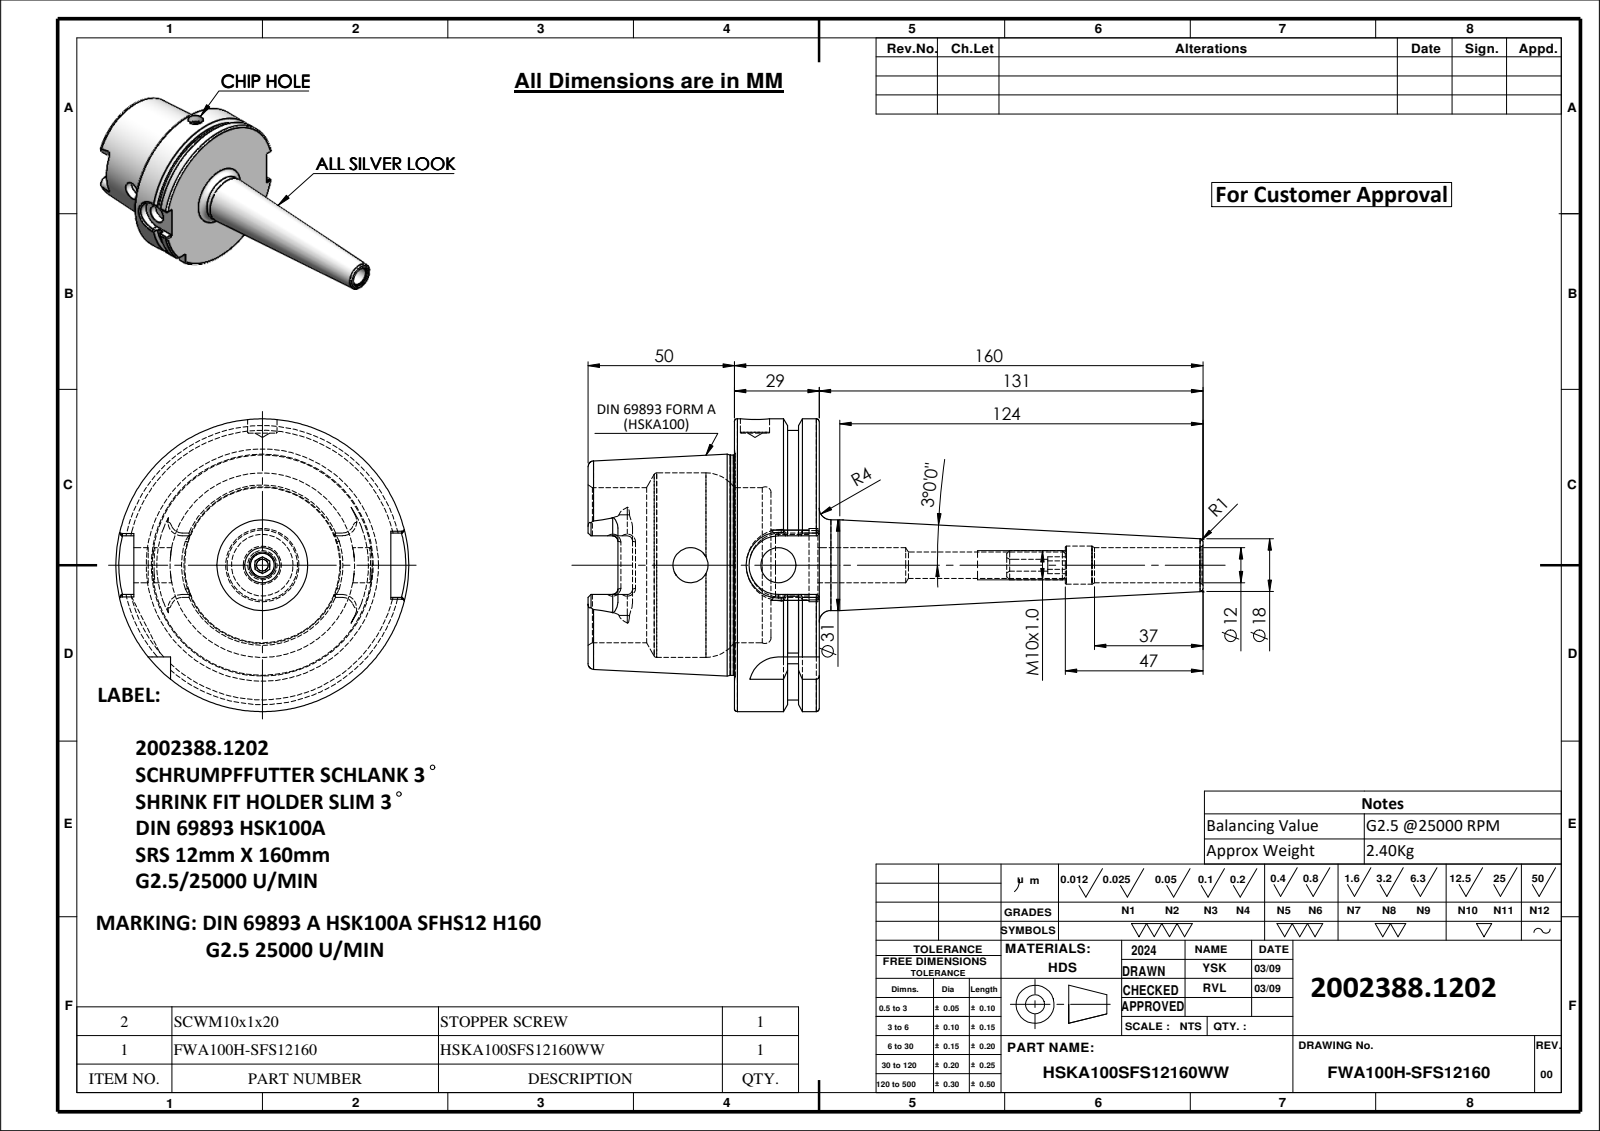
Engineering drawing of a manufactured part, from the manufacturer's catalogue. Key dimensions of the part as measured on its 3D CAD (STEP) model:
Part name (STEP PRODUCT): FWA100H-SFS12160; HSKA100SFS12160WW; SCWM10X1
STEP written by: SolidWorks 2024 (CONFIG_CONTROL_DESIGN)
Units: millimetres
Bodies: 2 solids, 205 faces (61 planar, 58 cylindrical, 86 other)
Overall size (bounding box): 210 × 100 × 100
Volume: 307 979 mm³ · Surface area: 64 780 mm²
Round holes (diameter × count): ⌀12 ×3, ⌀4 ×1, ⌀9 ×1, ⌀10 ×1, ⌀13 ×1, ⌀21 ×1, ⌀25 ×1, ⌀53 ×1, ⌀63 ×1
Round bosses / shafts (diameter × count): ⌀100 ×1, ⌀92 ×1, ⌀75.16 ×1, ⌀31 ×1, ⌀10 ×1
Partial cylindrical surfaces — rounded edges, fillets, slot ends (radius × count): R1.8 ×6, R4.88 ×4, R10 ×2, R11 ×1
Main face-to-face distances: 28.95, 12.5, 16.45, 50, 62.5, 78.95, 71.87, 21.87, 9.37, 7.08
Hole centre spacings: 30
